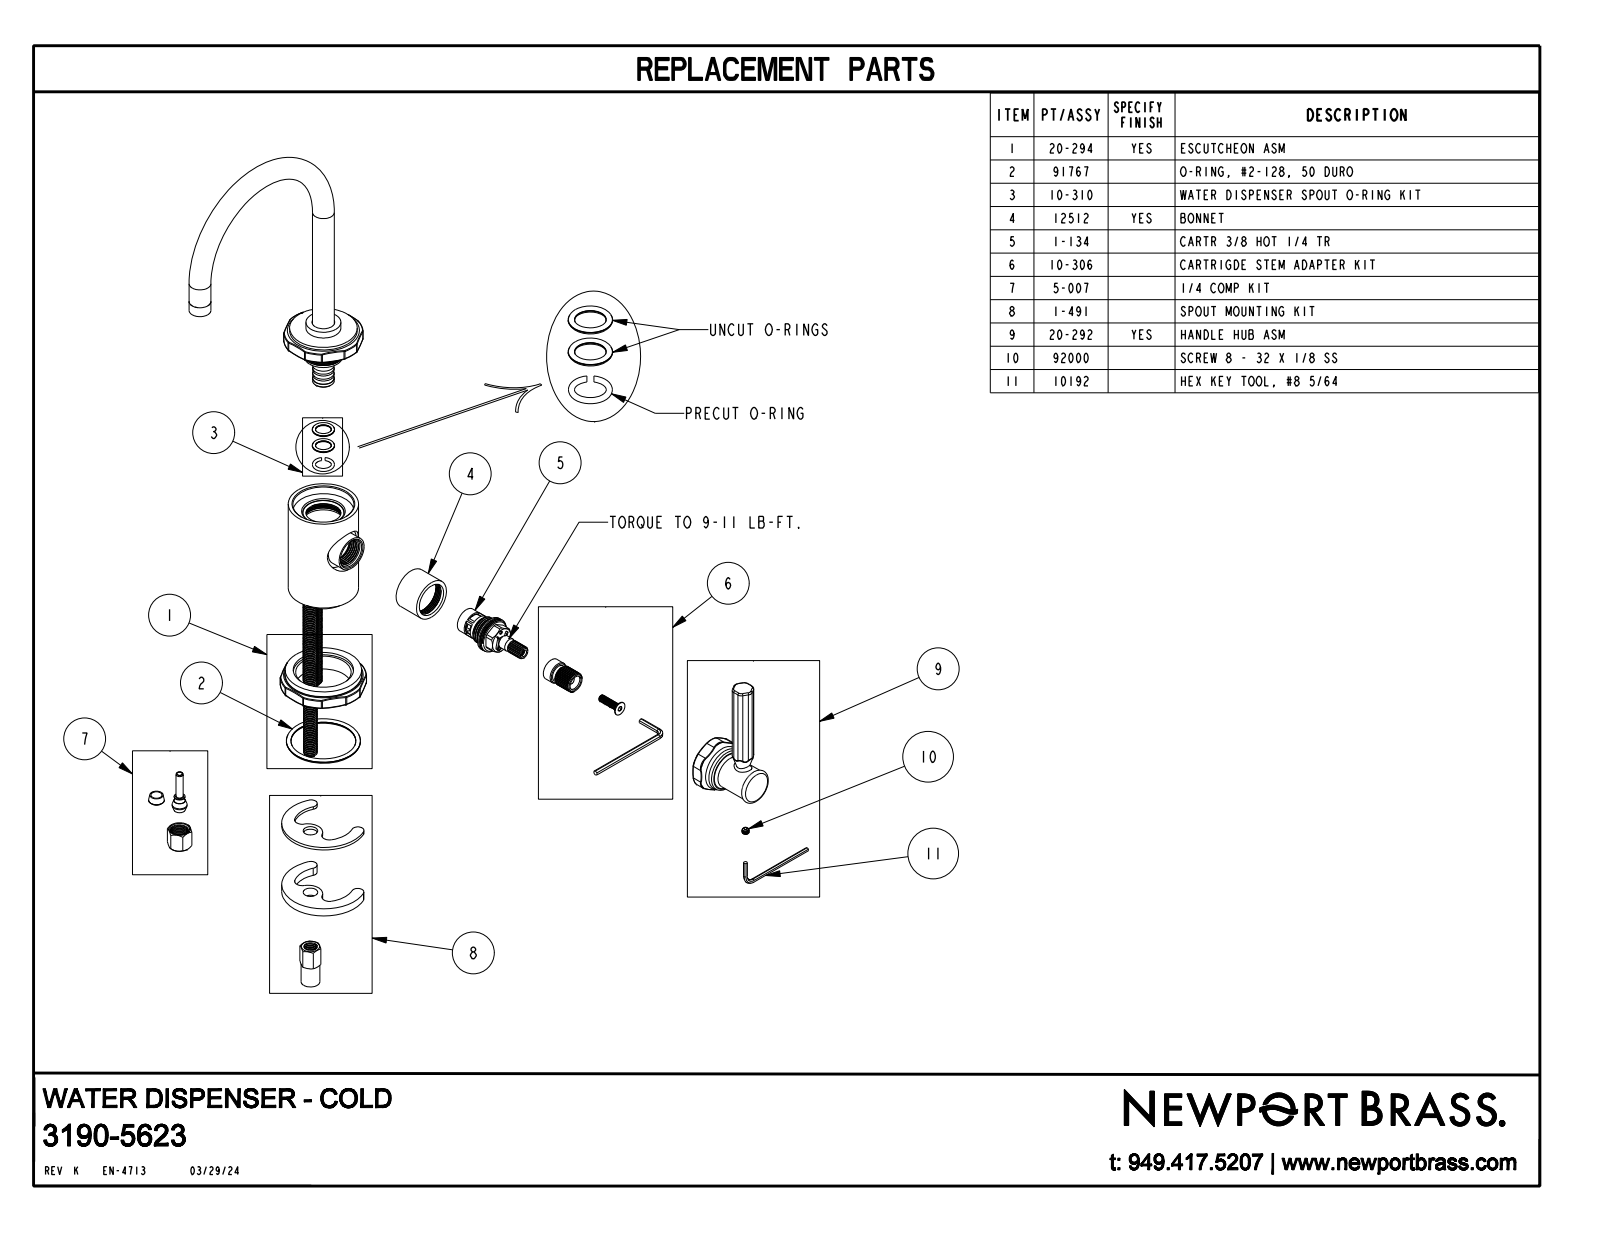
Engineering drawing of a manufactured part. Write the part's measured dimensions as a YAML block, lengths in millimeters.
part_name: "3190-5623"
step_written_by: "CREO PARAMETRIC BY PTC INC, 2018400 (CONFIG_CONTROL_DESIGN)"
units: millimeters
bodies: {solids: 1, faces: 306, planar: 36, cylindrical: 66, other: 204}
overall_size: [234.3, 132, 90.2]
volume: 171600
surface_area: 31880
round_holes:
  - {diameter: 25.4, count: 1}
round_bosses_or_shafts:
  - {diameter: 12.7, count: 2}
  - {diameter: 44.5, count: 1}
  - {diameter: 40.9, count: 1}
  - {diameter: 39.4, count: 1}
  - {diameter: 24.6, count: 1}
  - {diameter: 20.3, count: 1}
  - {diameter: 19.3, count: 1}
partial_cylinders:
  - {radius: 2, count: 24}
  - {radius: 3, count: 6}
  - {radius: 7.9, count: 6}
  - {radius: 23.1, count: 1}
  - {radius: 25.1, count: 1}
face_to_face_distances: [78.6, 1.9, 46.1, 11.9, 10.8, 67.8, 48, 44.1, 82.7, 71.9]
